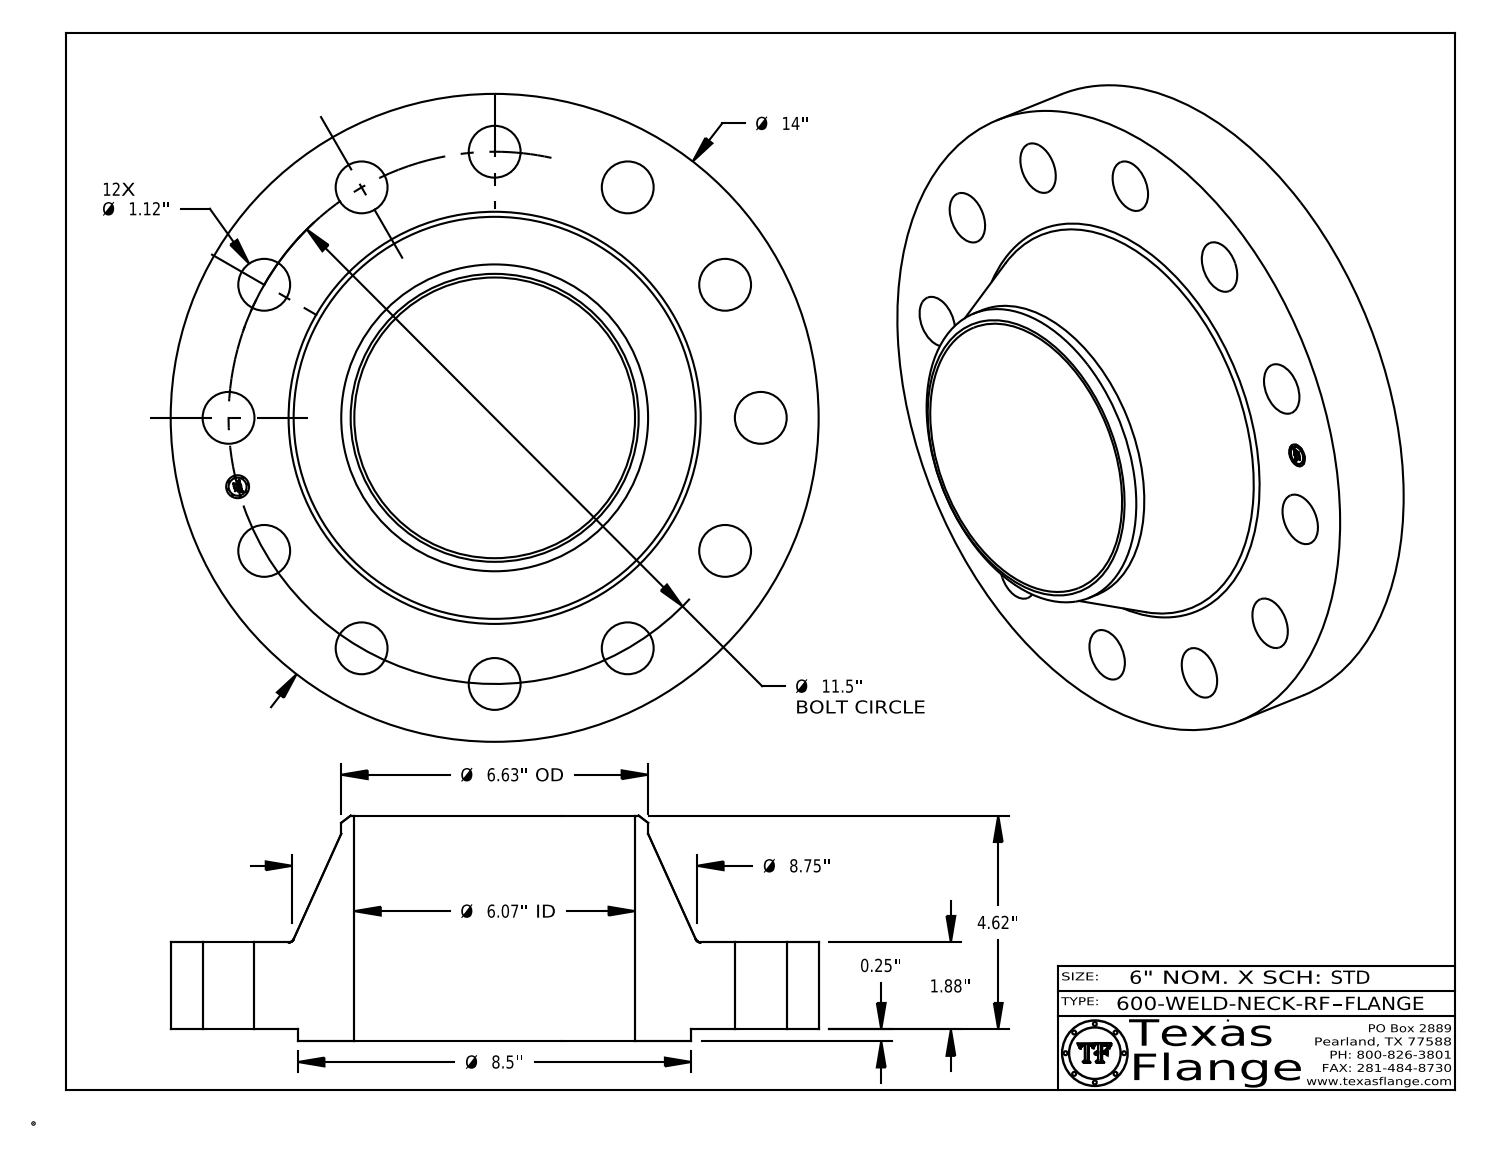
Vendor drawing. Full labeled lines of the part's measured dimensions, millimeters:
Part name (STEP PRODUCT): 600-WELD-NECK-RF
STEP written by: CATIA V5 STEP AP214 (AUTOMOTIVE_DESIGN)
Units: millimetres
Bodies: 1 solid, 427 faces (369 planar, 52 cylindrical, 6 other)
Overall size (bounding box): 355.6 × 355.6 × 123.7
Volume: 4 320 000 mm³ · Surface area: 342 100 mm²
Round holes (diameter × count): ⌀28.4 ×12, ⌀12.6 ×1, ⌀154.1 ×1
Round bosses / shafts (diameter × count): ⌀0.8 ×8, ⌀355.6 ×1, ⌀215.9 ×1, ⌀168.4 ×1, ⌀9.9 ×1
Main face-to-face distances: 47.8, 6.4, 54.1, 123.7, 117.3, 69.6, 53.7, 47.4, 0.4, 70
Hole centre spacings: 146.1, 206.6, 282.1, 75.6, 146.1, 253, 292.1, 75.6
